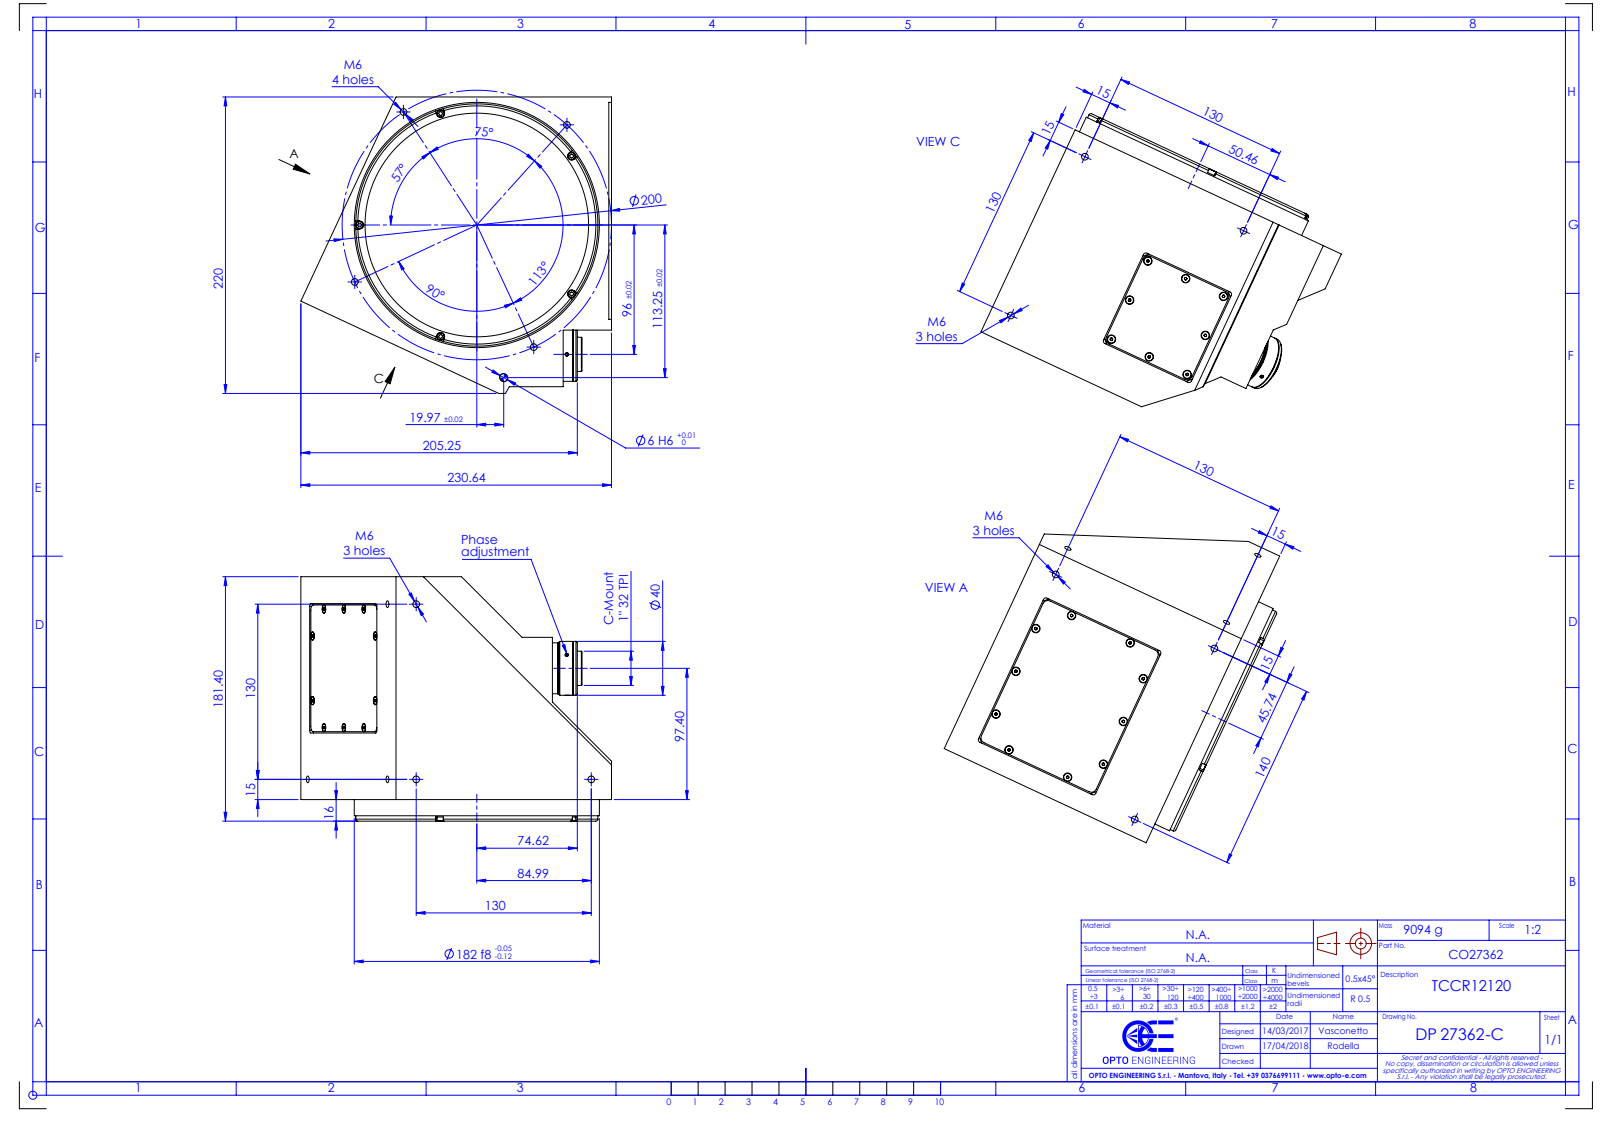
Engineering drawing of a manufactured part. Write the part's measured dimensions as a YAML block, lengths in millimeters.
part_name: "DP27362_TCCR12120"
step_written_by: "SolidWorks 2021 (CONFIG_CONTROL_DESIGN)"
units: millimeters
bodies: {solids: 0, faces: 492, planar: 211, cylindrical: 144, other: 137}
overall_size: [230.64, 220, 181.4]
round_holes:
  - {diameter: 5, count: 13}
  - {diameter: 1.8, count: 2}
  - {diameter: 6, count: 1}
  - {diameter: 14.5, count: 1}
  - {diameter: 22, count: 1}
  - {diameter: 22.5, count: 1}
  - {diameter: 166, count: 1}
  - {diameter: 170.8, count: 1}
round_bosses_or_shafts:
  - {diameter: 5.75, count: 25}
  - {diameter: 5.5, count: 5}
  - {diameter: 182, count: 1}
  - {diameter: 179.8, count: 1}
  - {diameter: 40, count: 1}
  - {diameter: 38.2, count: 1}
  - {diameter: 37.8, count: 1}
  - {diameter: 25.4, count: 1}
partial_cylinders:
  - {radius: 4, count: 10}
  - {radius: 2, count: 8}
  - {radius: 3, count: 5}
face_to_face_distances: [165.4, 0.44, 0.56, 2, 215, 165, 50, 8, 4, 19.99]
hole_center_spacings: [130, 100, 10, 20, 31.76, 99.99, 115, 121.75]
